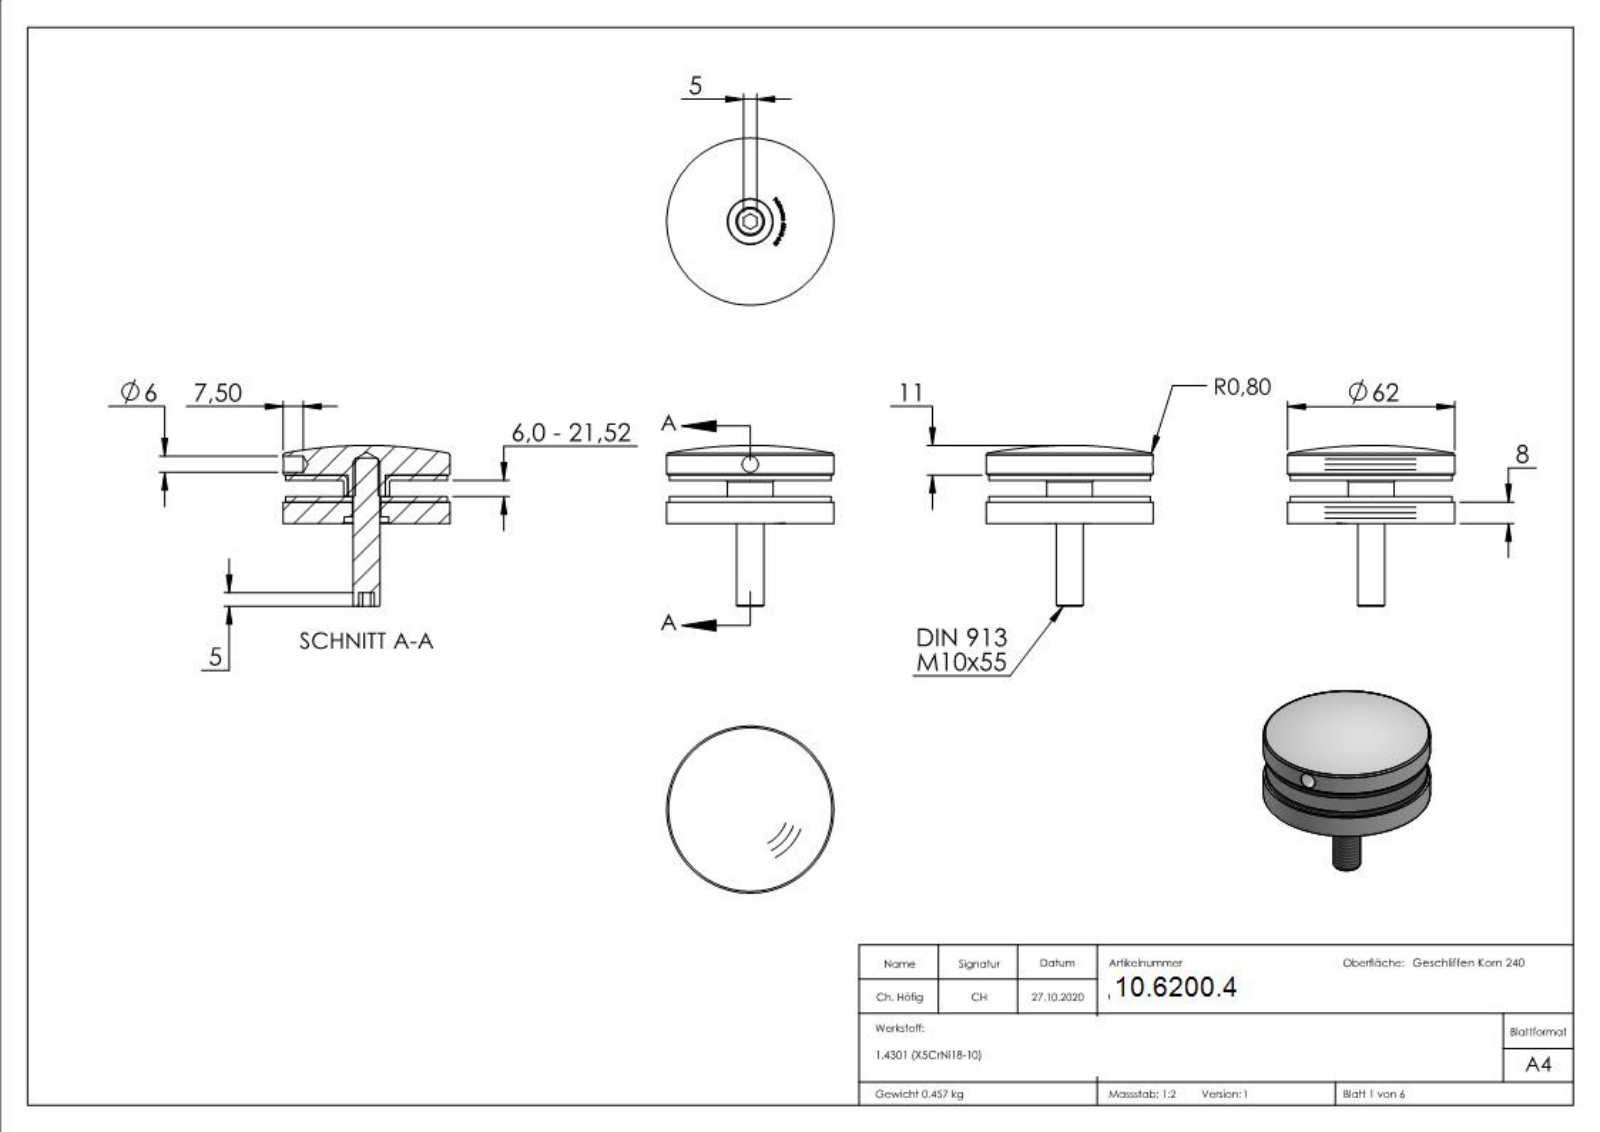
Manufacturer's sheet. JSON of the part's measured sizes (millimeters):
{"part_name": "60240-240 Teil4; 60240-240 Teil1; 60240-240 Teil3_60240-240 Teil3; 60240-240 Teil3 (+7 more)", "step_written_by": "SolidWorks 2018 (CONFIG_CONTROL_DESIGN)", "units": "millimeters", "bodies": {"solids": 5, "faces": 292, "planar": 144, "cylindrical": 26, "other": 122}, "overall_size": [80, 62, 62], "volume_mm3": 67349, "surface_area_mm2": 30320, "round_holes": [[6, 1], [8.5, 1], [10.5, 1], [14, 1], [16.5, 1]], "round_bosses_or_shafts": [[62, 1], [60, 1], [17, 1], [10, 1]], "face_to_face_distances": [8, 10, 2, 18, 16, 6, 2.5, 5.5, 7.5, 13.5]}
